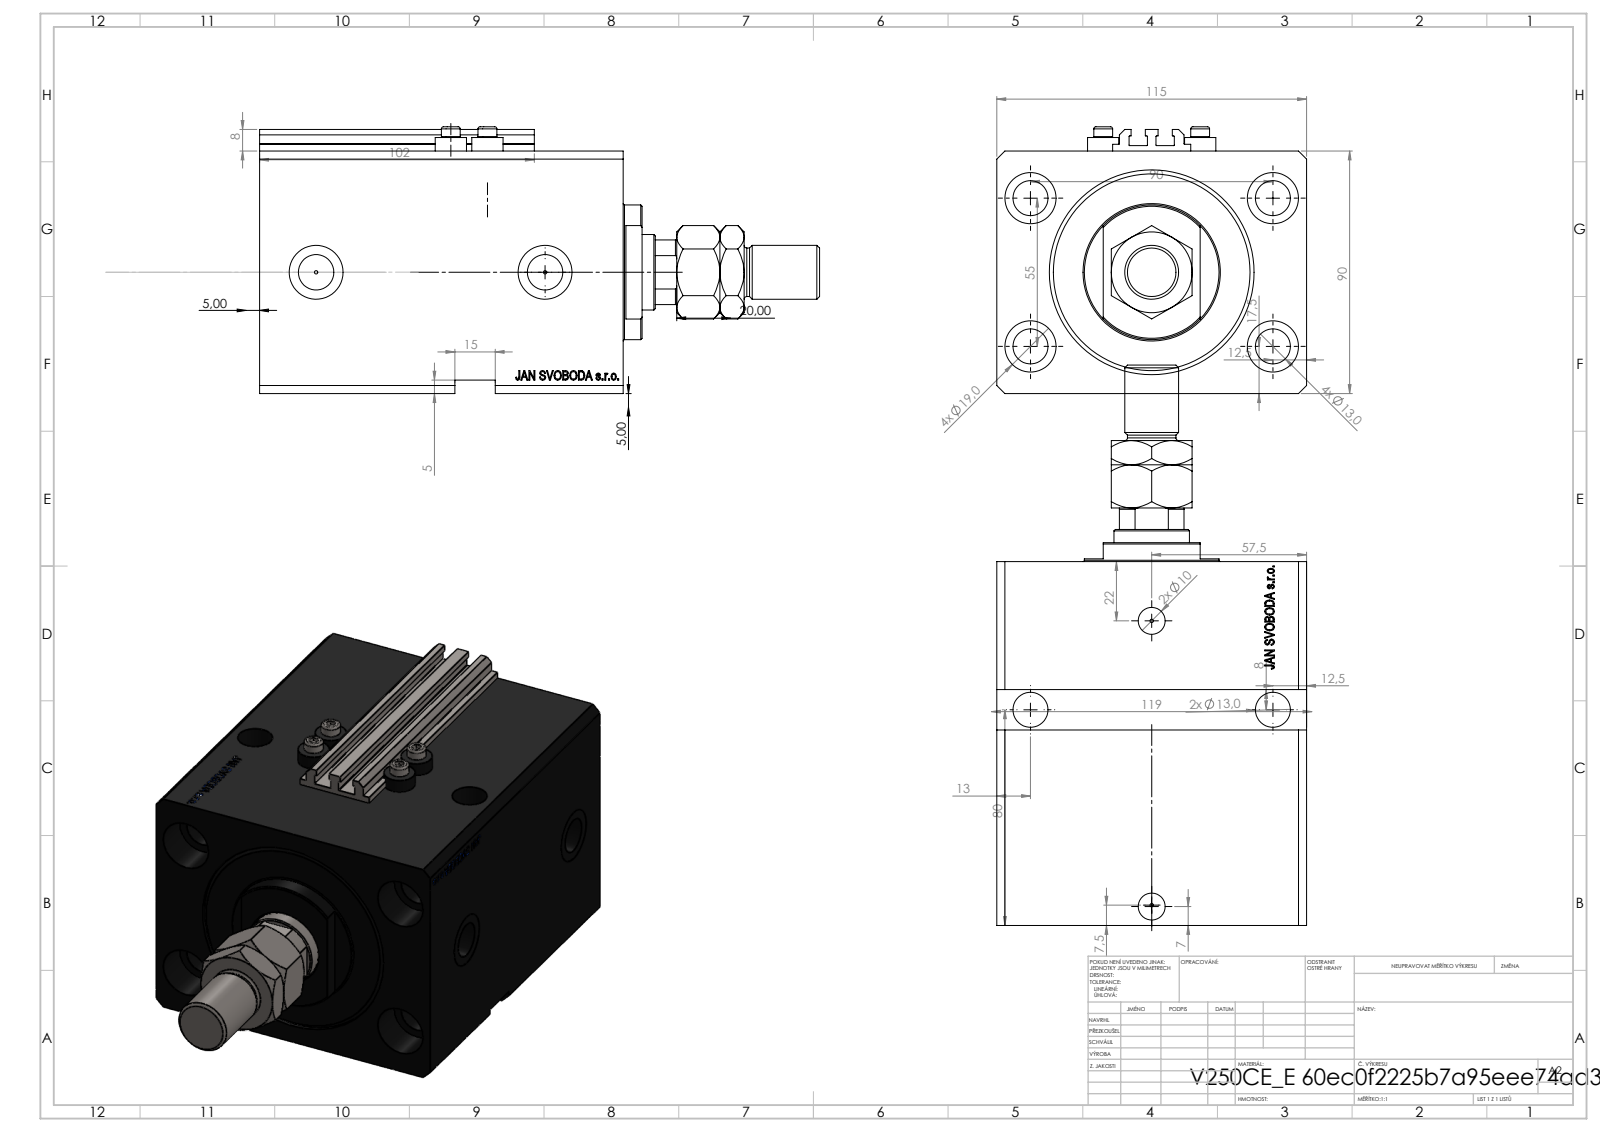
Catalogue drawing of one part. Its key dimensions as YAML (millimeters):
part_name: "V250CE_C_VCP; V250CE_E_Body; ALLEN BOLT V250CE; V250CE_VC_E (+1 more)"
step_written_by: "SolidWorks 2019 (CONFIG_CONTROL_DESIGN)"
units: millimeters
bodies: {solids: 9, faces: 1192, planar: 562, cylindrical: 162, other: 468}
overall_size: [208, 115, 99]
volume: 1184000
surface_area: 193697
round_holes:
  - {diameter: 13, count: 8}
  - {diameter: 1.25, count: 4}
  - {diameter: 4, count: 4}
  - {diameter: 19, count: 4}
  - {diameter: 10, count: 2}
  - {diameter: 13.16, count: 2}
  - {diameter: 20, count: 2}
  - {diameter: 18.5, count: 1}
  - {diameter: 28, count: 1}
  - {diameter: 63, count: 1}
  - {diameter: 76, count: 1}
round_bosses_or_shafts:
  - {diameter: 11.6, count: 4}
  - {diameter: 7, count: 4}
  - {diameter: 50, count: 1}
  - {diameter: 20, count: 1}
  - {diameter: 18, count: 1}
partial_cylinders:
  - {radius: 0.2, count: 10}
  - {radius: 13.5, count: 1}
face_to_face_distances: [115, 90, 20, 135, 17.9, 117.1, 97.1, 65, 13, 47.1]
hole_center_spacings: [52.74, 55.8, 85.76, 90, 13.6, 27.39, 28.46, 33.62]
